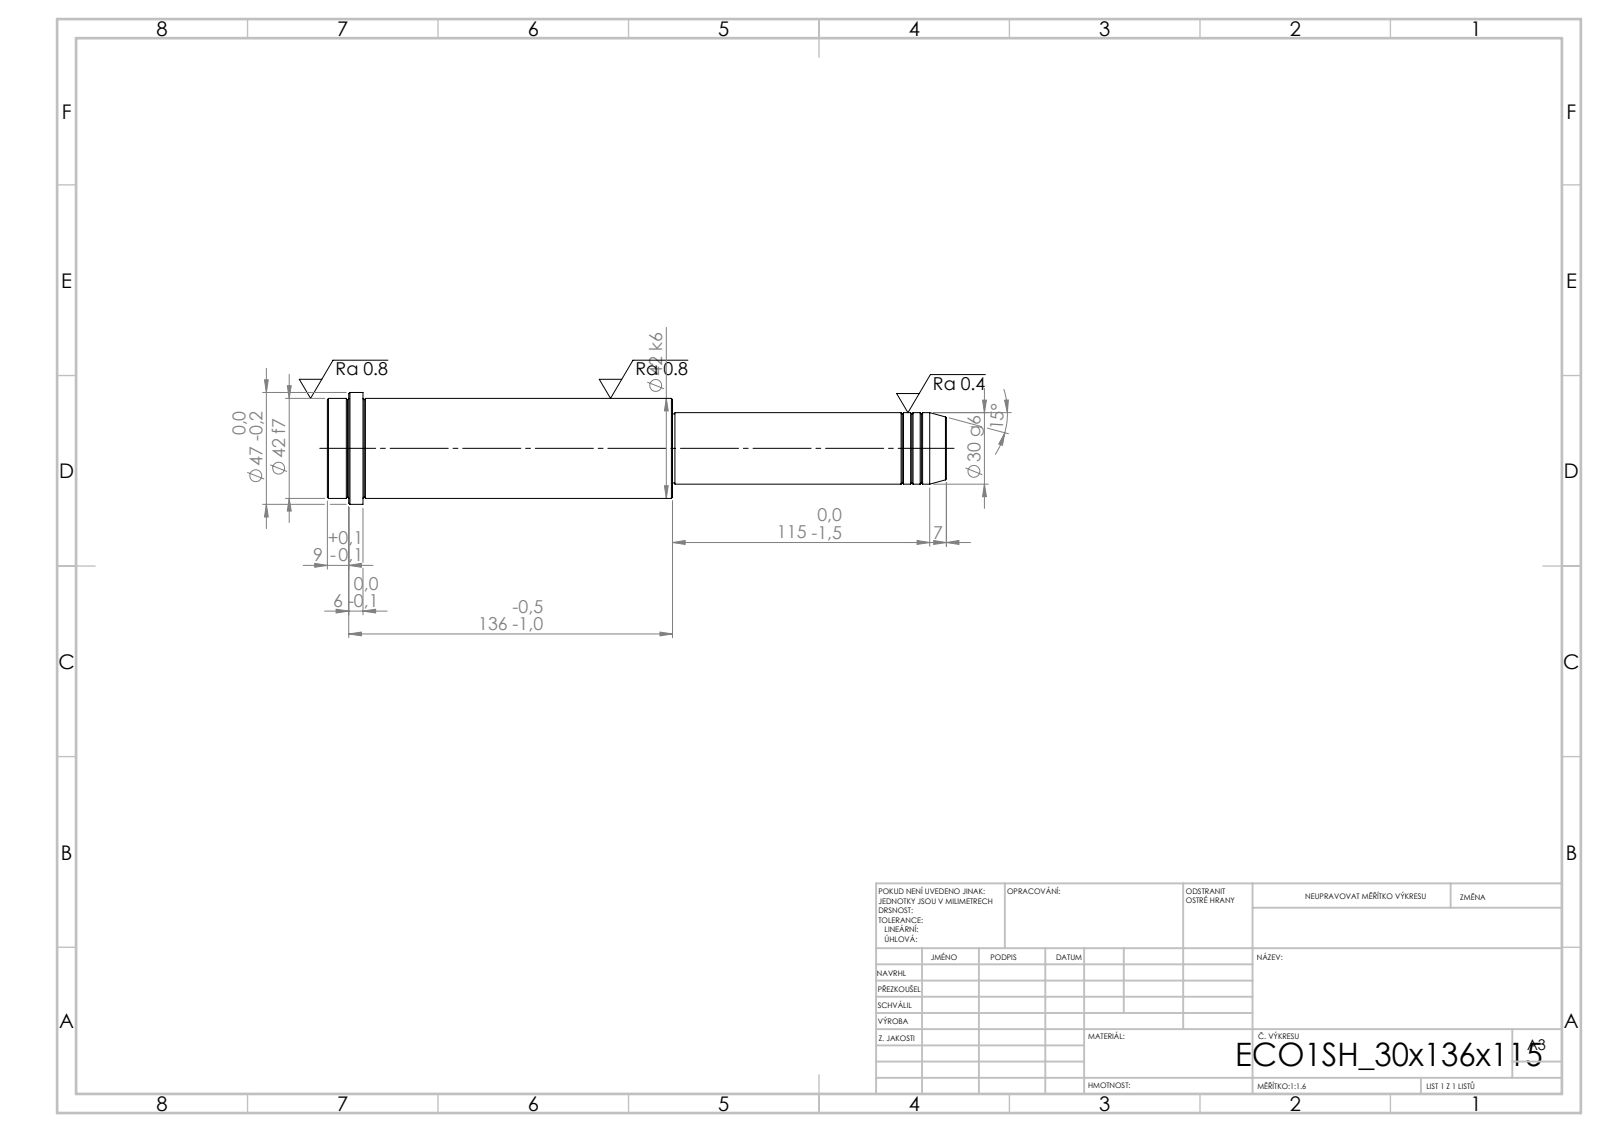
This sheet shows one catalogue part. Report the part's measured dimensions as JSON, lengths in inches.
{"step_written_by": "SolidWorks 2019 (CONFIG_CONTROL_DESIGN)", "units": "inches", "bodies": {"solids": 1, "faces": 52, "planar": 6, "cylindrical": 16, "other": 30}, "overall_size": [10.236, 1.85, 1.85], "volume_in3": 17.29, "surface_area_in2": 52.09, "round_bosses_or_shafts": [[1.85, 1], [1.654, 1], [1.181, 1], [1.142, 1]], "face_to_face_distances": [5.709, 4.528, 10.236, 9.646, 5.118, 0.591, 9.882, 5.354, 0.236, 0.354]}
